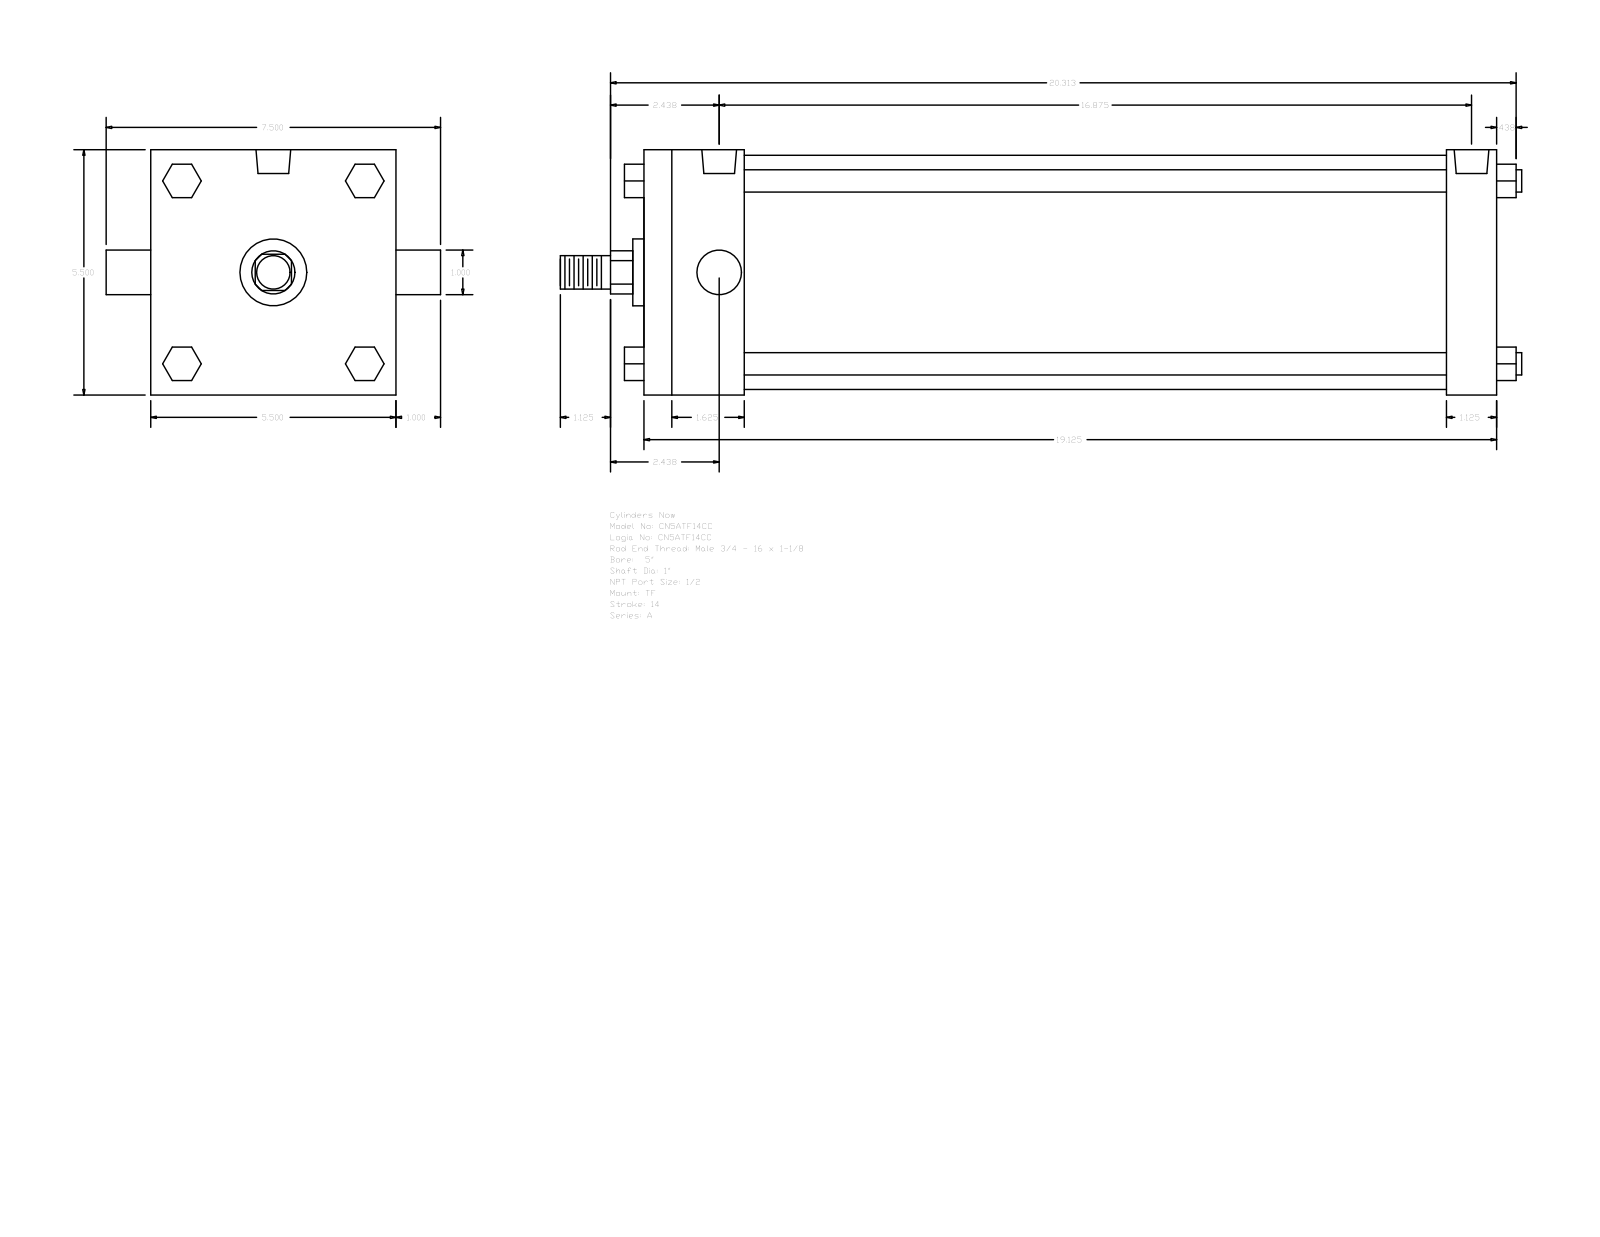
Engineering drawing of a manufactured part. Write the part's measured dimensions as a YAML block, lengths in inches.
part_name: "A_TF__0500_1"
step_written_by: "GSSL Pune (CONFIG_CONTROL_DESIGN)"
units: inches
bodies: {solids: 0, faces: 120, planar: 92, cylindrical: 28, other: 0}
overall_size: [21.563, 7.5, 5.5]
round_holes:
  - {diameter: 0.344, count: 3}
  - {diameter: 0.778, count: 2}
round_bosses_or_shafts:
  - {diameter: 0.5, count: 4}
  - {diameter: 1, count: 2}
  - {diameter: 5.25, count: 1}
  - {diameter: 1.5, count: 1}
  - {diameter: 0.75, count: 1}
partial_cylinders:
  - {radius: 0.484, count: 1}
face_to_face_distances: [5.5, 19.125, 1.125, 18, 2.25, 15.75, 16.875, 0.75, 2.05, 3.55]
hole_center_spacings: [0.094, 16.781, 16.687, 16.875]
